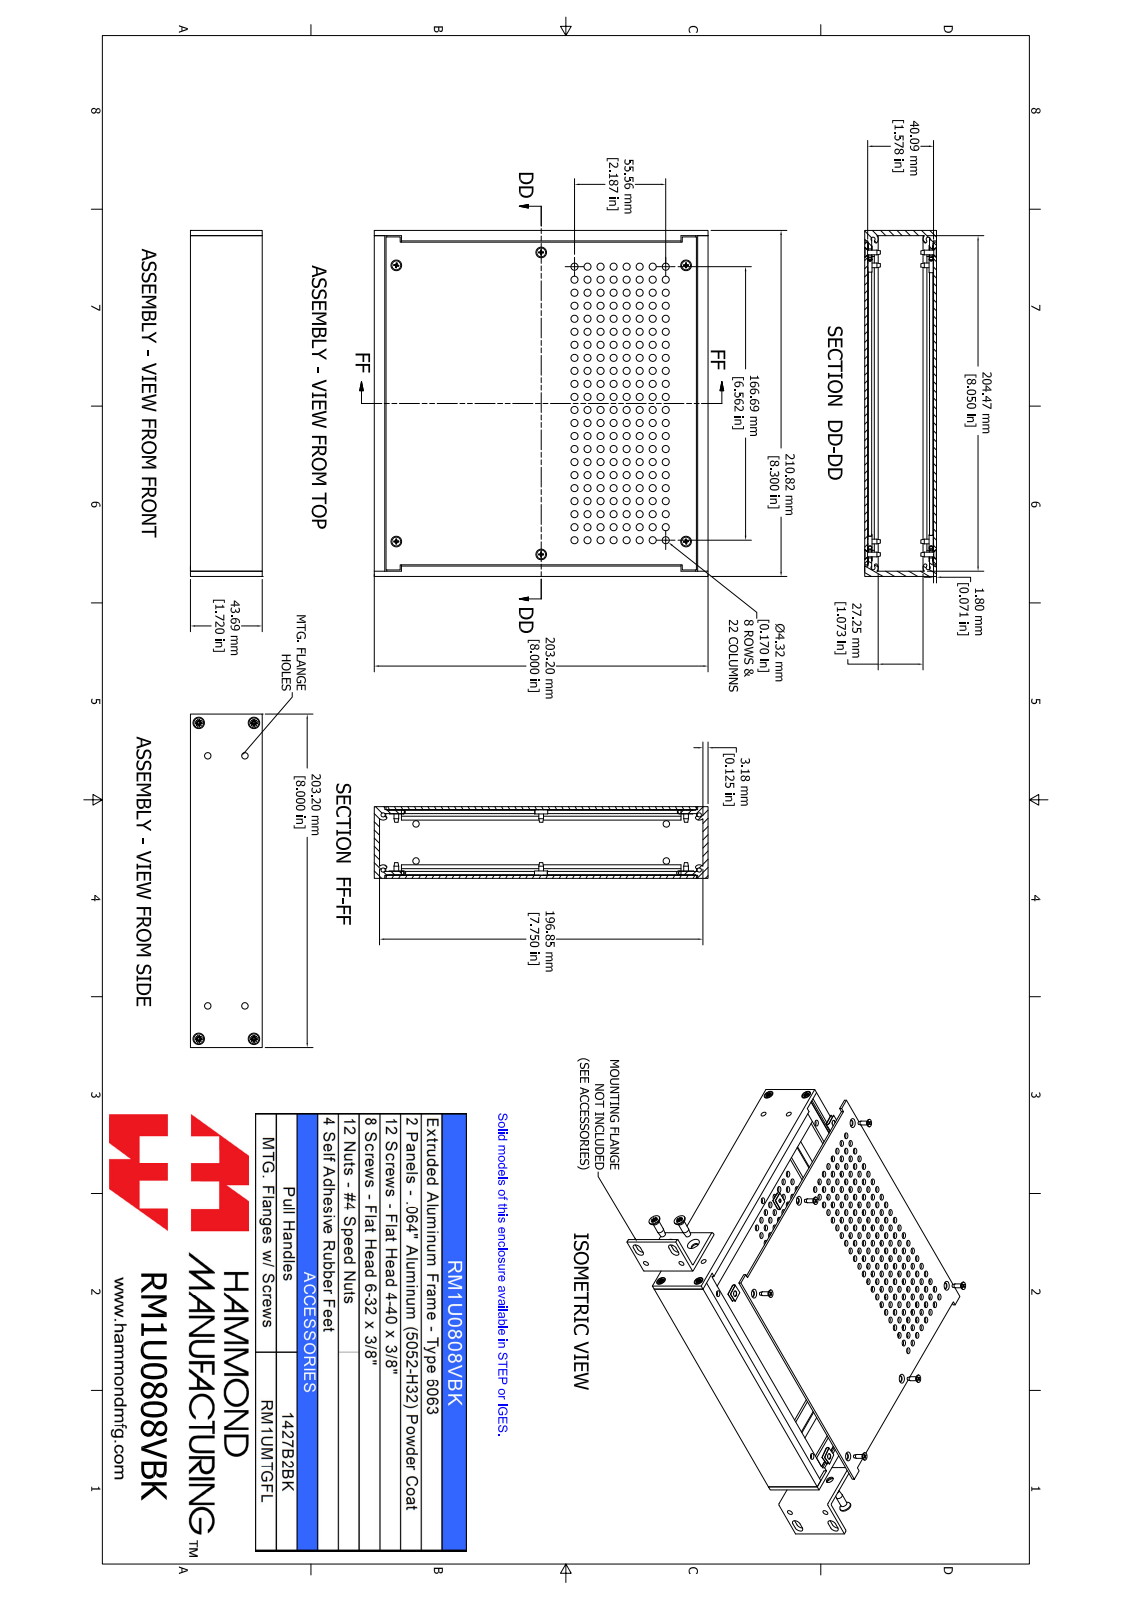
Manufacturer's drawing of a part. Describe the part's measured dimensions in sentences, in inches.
The part is named "RM1U0808VBK". Its 3-D file was written by "SolidWorks 2021 (AUTOMOTIVE_DESIGN)". It is 38 solids with 1328 faces: 468 planar, 508 cylindrical and 352 other. Overall it measures 8.3 by 8 by 1.72 inches. Its volume is 18.6 cubic inches and its surface area 443.7 square inches. Round holes: 176 of diameter 0.17, 6 of diameter 0.098, 6 of diameter 0.157, 6 of diameter 0.169, 4 of diameter 0.138, 4 of diameter 0.156. Round bosses or shafts: 6 of diameter 0.214, 6 of diameter 0.112, 4 of diameter 0.238, 4 of diameter 0.138. Partial cylindrical surfaces (rounded edges, fillets, slot ends): 12 of radius 0.039, 12 of radius 0.049, 8 of radius 0.05, 8 of radius 0.125, 7 of radius 0.038, 4 of radius 0.037. The main face-to-face distances are 0.071, 1.649, 1.72, 1.578, 0.125, 1.482, 0.167, 1.553, 0.096, 1.466. The hole center spacings are 0.313, 0.699, 0.442, 1.289, 0.988, 1.25, 0.937, 0.625.
